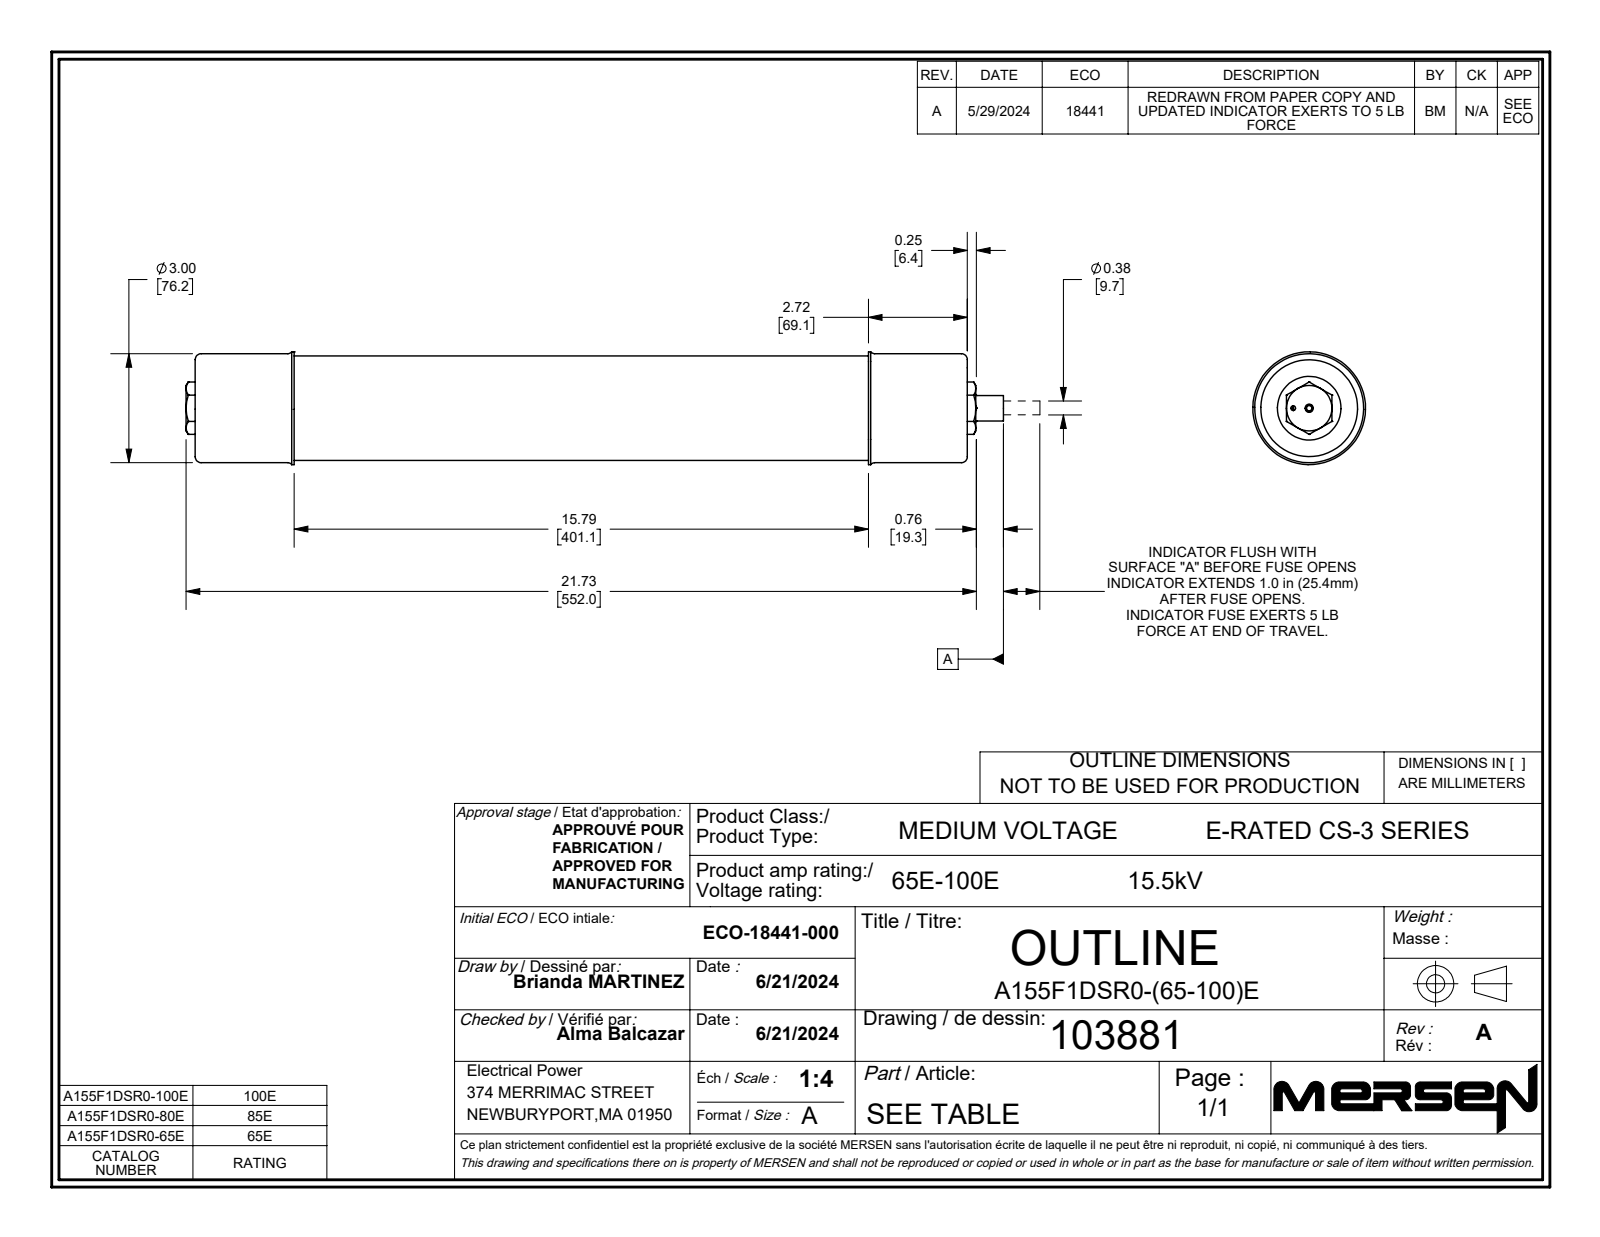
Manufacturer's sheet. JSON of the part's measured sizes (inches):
{"part_name": "36016_11378; 360025; 140018_-101; 9399_9399 (+5 more)", "step_written_by": "SolidWorks 2021 (AUTOMOTIVE_DESIGN)", "units": "inches", "bodies": {"solids": 7, "faces": 235, "planar": 55, "cylindrical": 101, "other": 79}, "overall_size": [22.476, 3.1, 3.1], "volume_in3": 27.5, "surface_area_in2": 507.2, "round_holes": [[0.125, 12], [0.129, 2], [0.069, 1], [0.146, 1], [0.188, 1], [0.391, 1], [0.465, 1], [0.512, 1], [0.906, 1], [2.625, 1], [2.89, 1]], "round_bosses_or_shafts": [[3.1, 1], [2.998, 1], [2.875, 1], [1.25, 1], [0.875, 1], [0.874, 1], [0.78, 1], [0.7, 1]], "face_to_face_distances": [0.054, 21.054, 0.085, 21.023, 0.031, 20.969, 21.108, 21, 0.016, 21.092], "hole_center_spacings": [20.38, 0.438, 0.876]}
